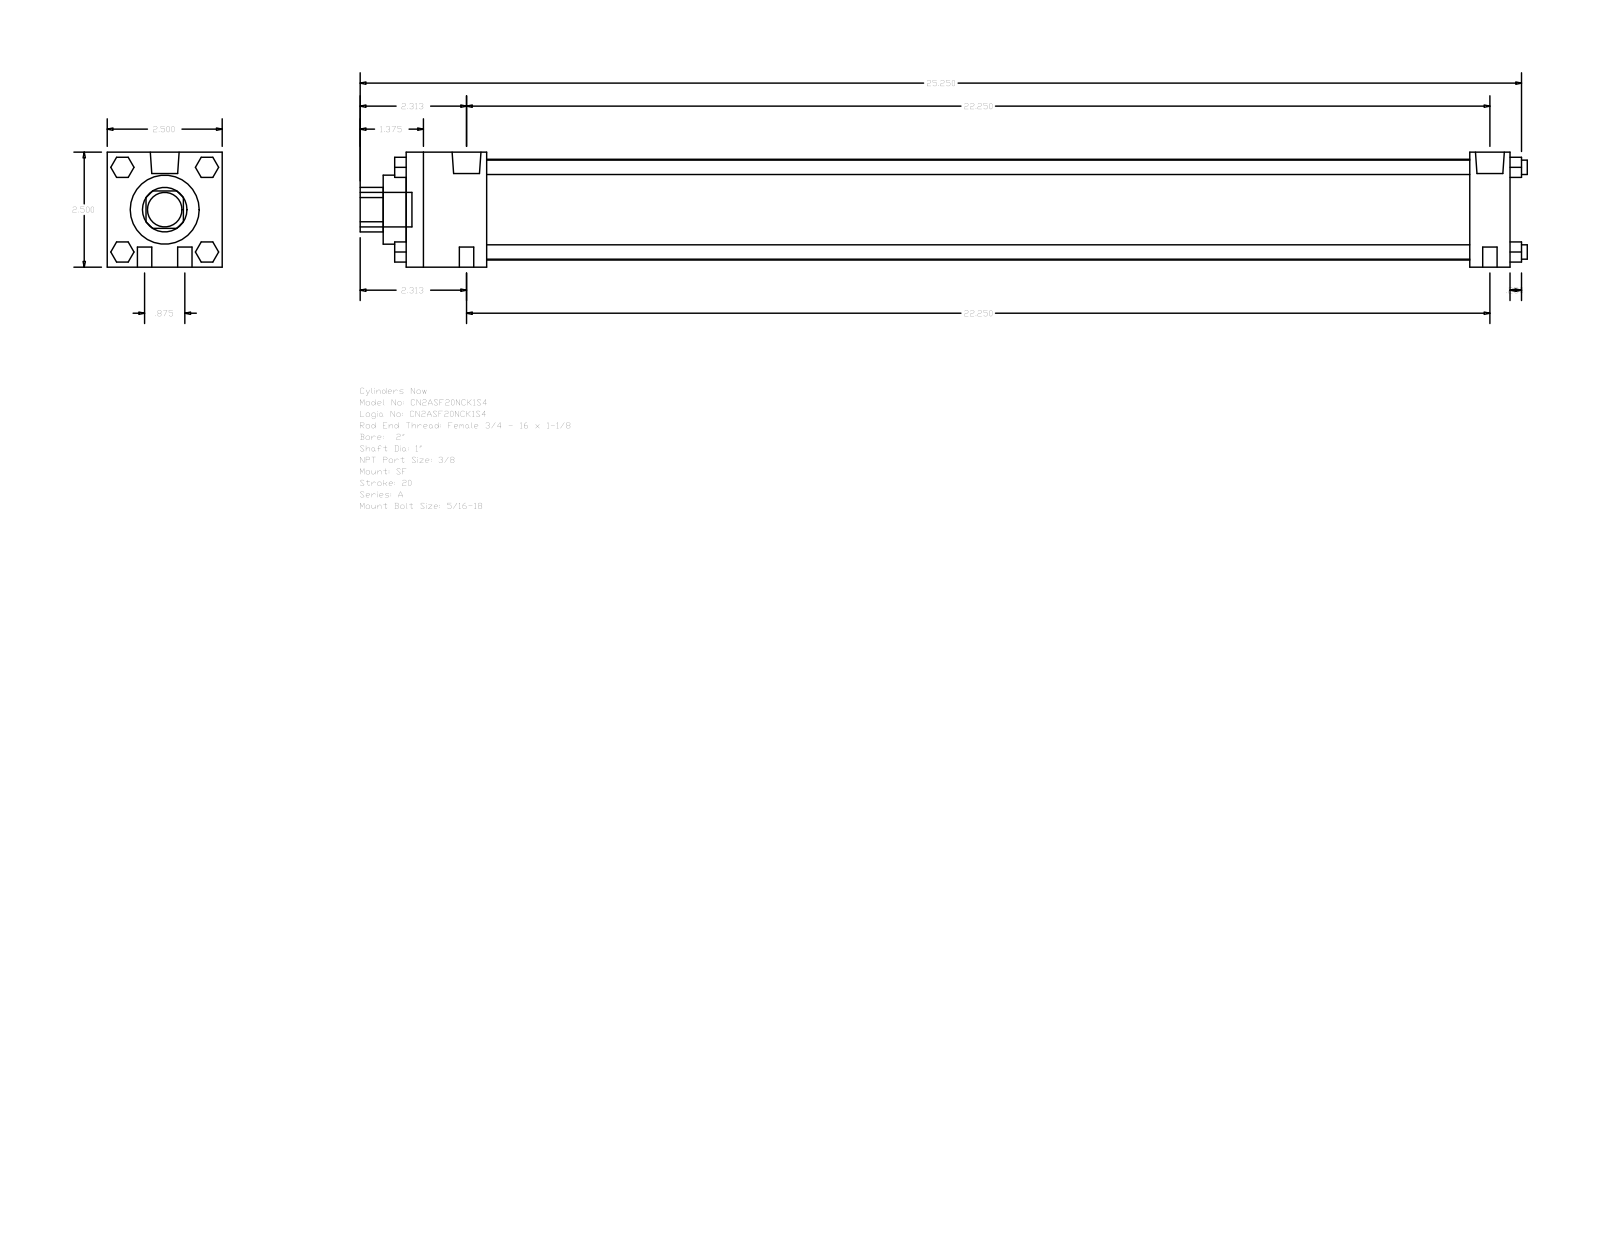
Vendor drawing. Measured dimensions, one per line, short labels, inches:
name: A_SF__0200_1
written by: GSSL Pune (CONFIG_CONTROL_DESIGN)
unit: in
bodies: 0 solids, 124 faces (94 planar, 30 cylindrical, 0 other)
size: 25.375 × 2.5 × 2.5
holes: 1× ⌀1, 1× ⌀1.5, 1× ⌀2.19
bosses: 8× ⌀0.313, 2× ⌀0.627, 2× ⌀0.219, 1× ⌀0.75
rounds: 1× R0.484
face distances: 2.5, 24, 23.125, 0.875, 1.75, 21.375, 22.25, 0.5, 24.5, 0.25
